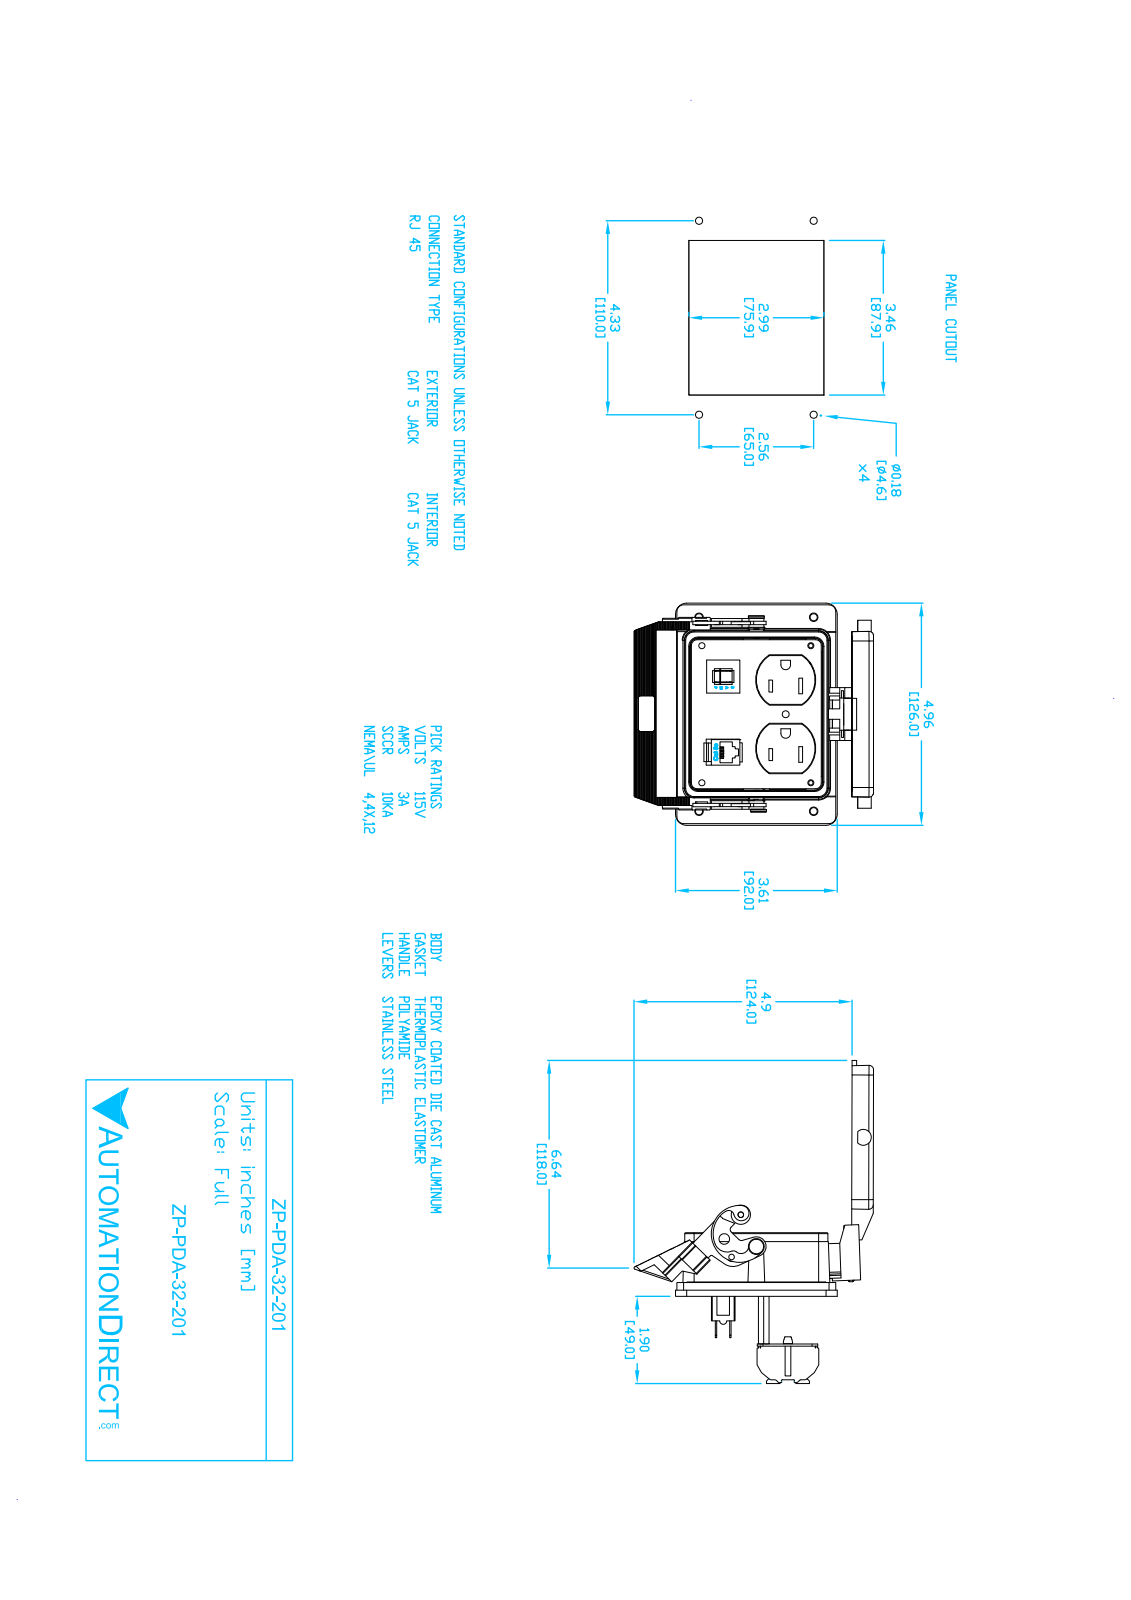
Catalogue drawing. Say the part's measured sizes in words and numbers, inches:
The part is named "ZP-PDA-32-201". Its 3-D file was written by "SolidWorks 2017 (AUTOMOTIVE_DESIGN)". It is 1 solid with 2862 faces: 1973 planar, 580 cylindrical and 309 other. Overall it measures 6.857 by 5.313 by 4.96 inches. Its volume is 13.15 cubic inches and its surface area 184.2 square inches. Round holes: 8 of diameter 0.098, 8 of diameter 0.144, 6 of diameter 0.173, 4 of diameter 0.16, 4 of diameter 0.19, 3 of diameter 0.091, 2 of diameter 0.097, 2 of diameter 0.12, 2 of diameter 0.126, 2 of diameter 0.138, 2 of diameter 0.202, 2 of diameter 0.228. Round bosses or shafts: 6 of diameter 0.226, 6 of diameter 0.22, 6 of diameter 0.118, 3 of diameter 0.205, 2 of diameter 0.354, 2 of diameter 0.344, 2 of diameter 0.096, 1 of diameter 0.43. Partial cylindrical surfaces (rounded edges, fillets, slot ends): 22 of radius 0.02, 18 of radius 0.1, 12 of radius 0.025, 12 of radius 0.25, 9 of radius 0.015, 8 of radius 0.125, 8 of radius 0.15, 6 of radius 0.01. The main face-to-face distances are 0.135, 0.907, 0.847, 0.06, 0.73, 1.577, 1.637, 0.977, 0.247, 0.6. The hole center spacings are 0.472, 0.236, 0.633, 1.063, 1.287, 1.378, 1.569, 2.578.
